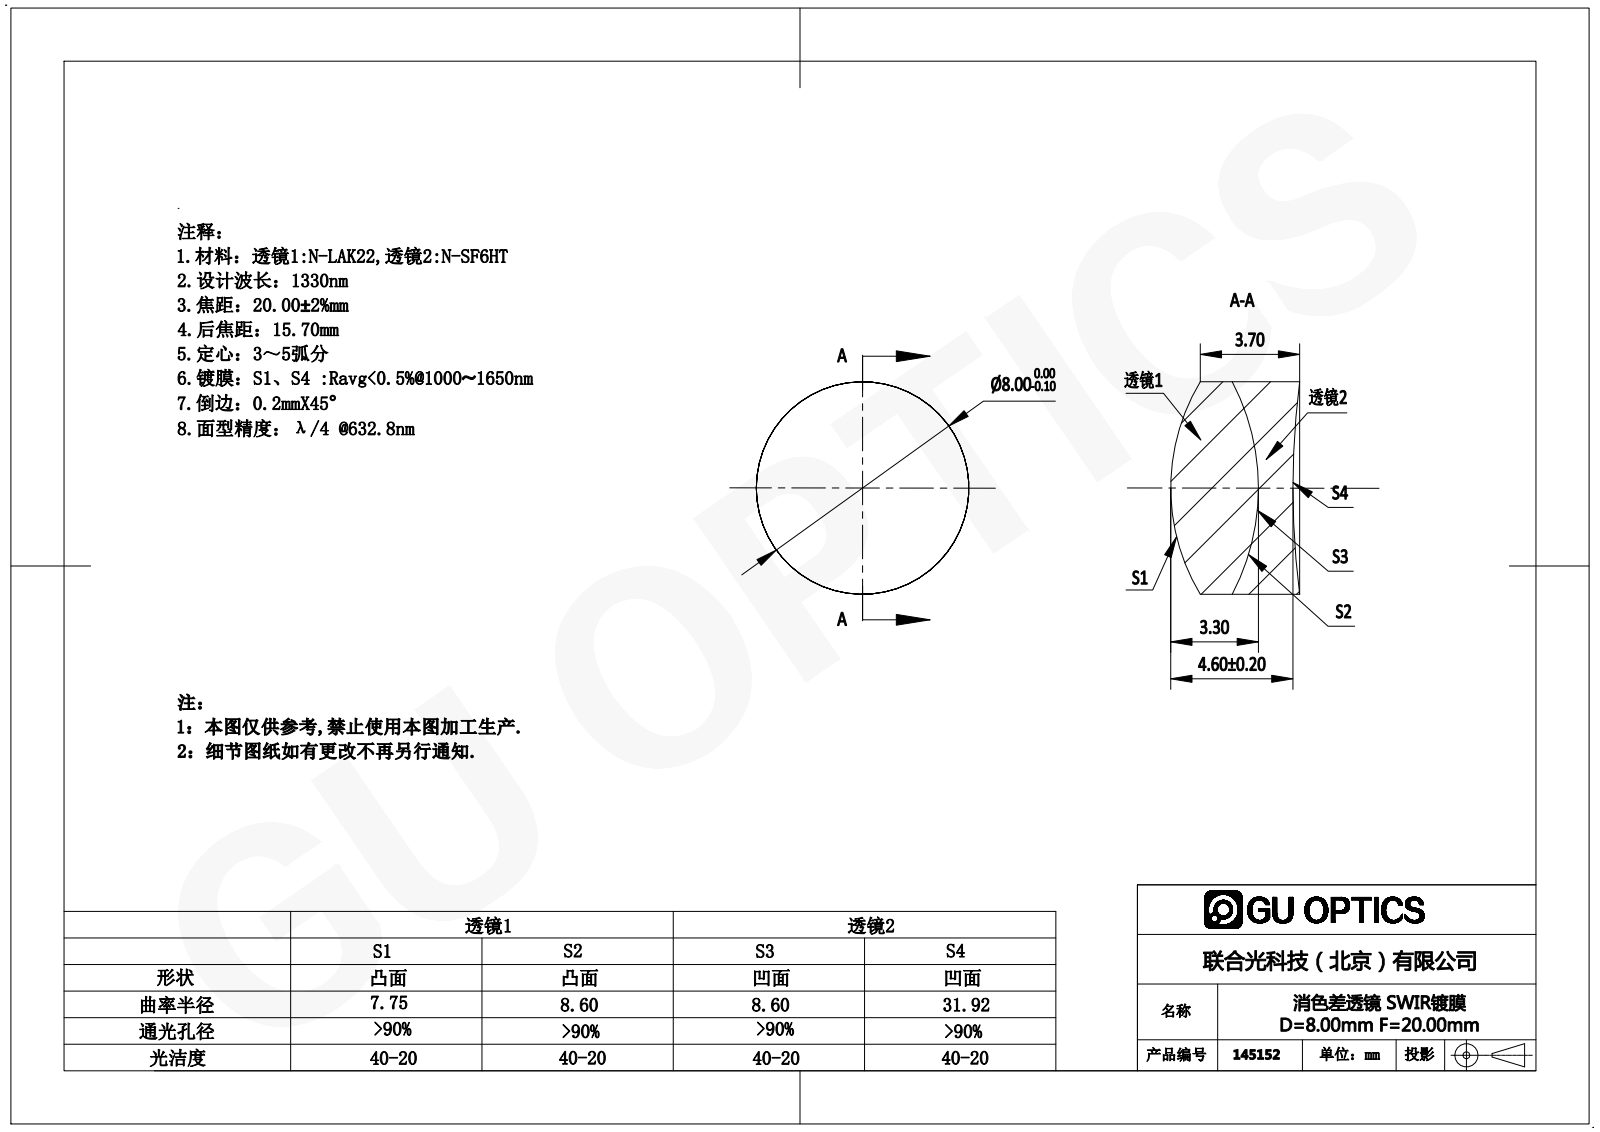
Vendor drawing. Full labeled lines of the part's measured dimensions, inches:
Part name (STEP PRODUCT): 145152
STEP written by: SolidWorks 2016 (AUTOMOTIVE_DESIGN)
Units: inches
Bodies: 2 solids, 12 faces (0 planar, 4 cylindrical, 8 other)
Overall size (bounding box): 0.315 × 0.315 × 0.191
Volume: 0.013 in³ · Surface area: 0.473 in²
Round bosses / shafts (diameter × count): ⌀0.315 ×1
